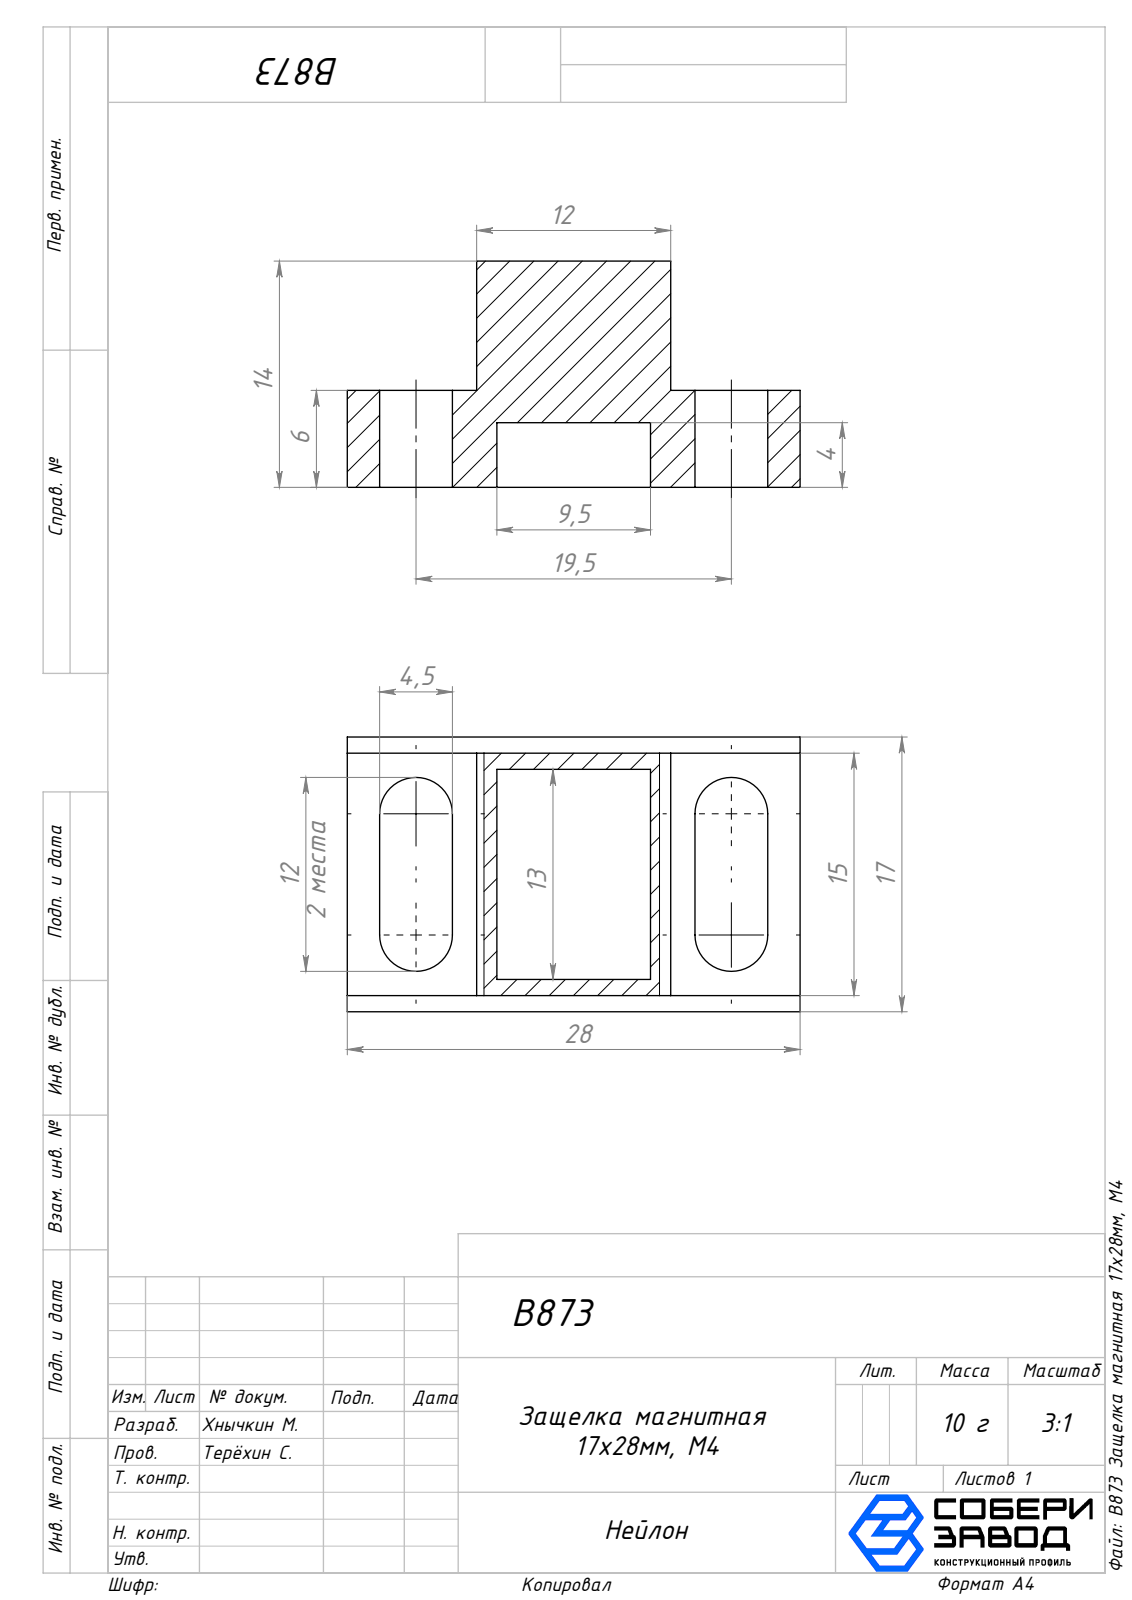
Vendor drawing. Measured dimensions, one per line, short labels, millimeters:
name: B873 Защелка магнитная 17х28мм, М4
written by: SolidWorks 2025 (AUTOMOTIVE_DESIGN)
unit: mm
bodies: 1 solid, 27 faces (23 planar, 4 cylindrical, 0 other)
size: 28 × 17 × 14
volume: 2 954 mm³; area: 2 237 mm²
rounds: 4× R2.25
face distances: 15, 8, 2, 14, 6, 20, 1, 1.5, 4.5, 4
